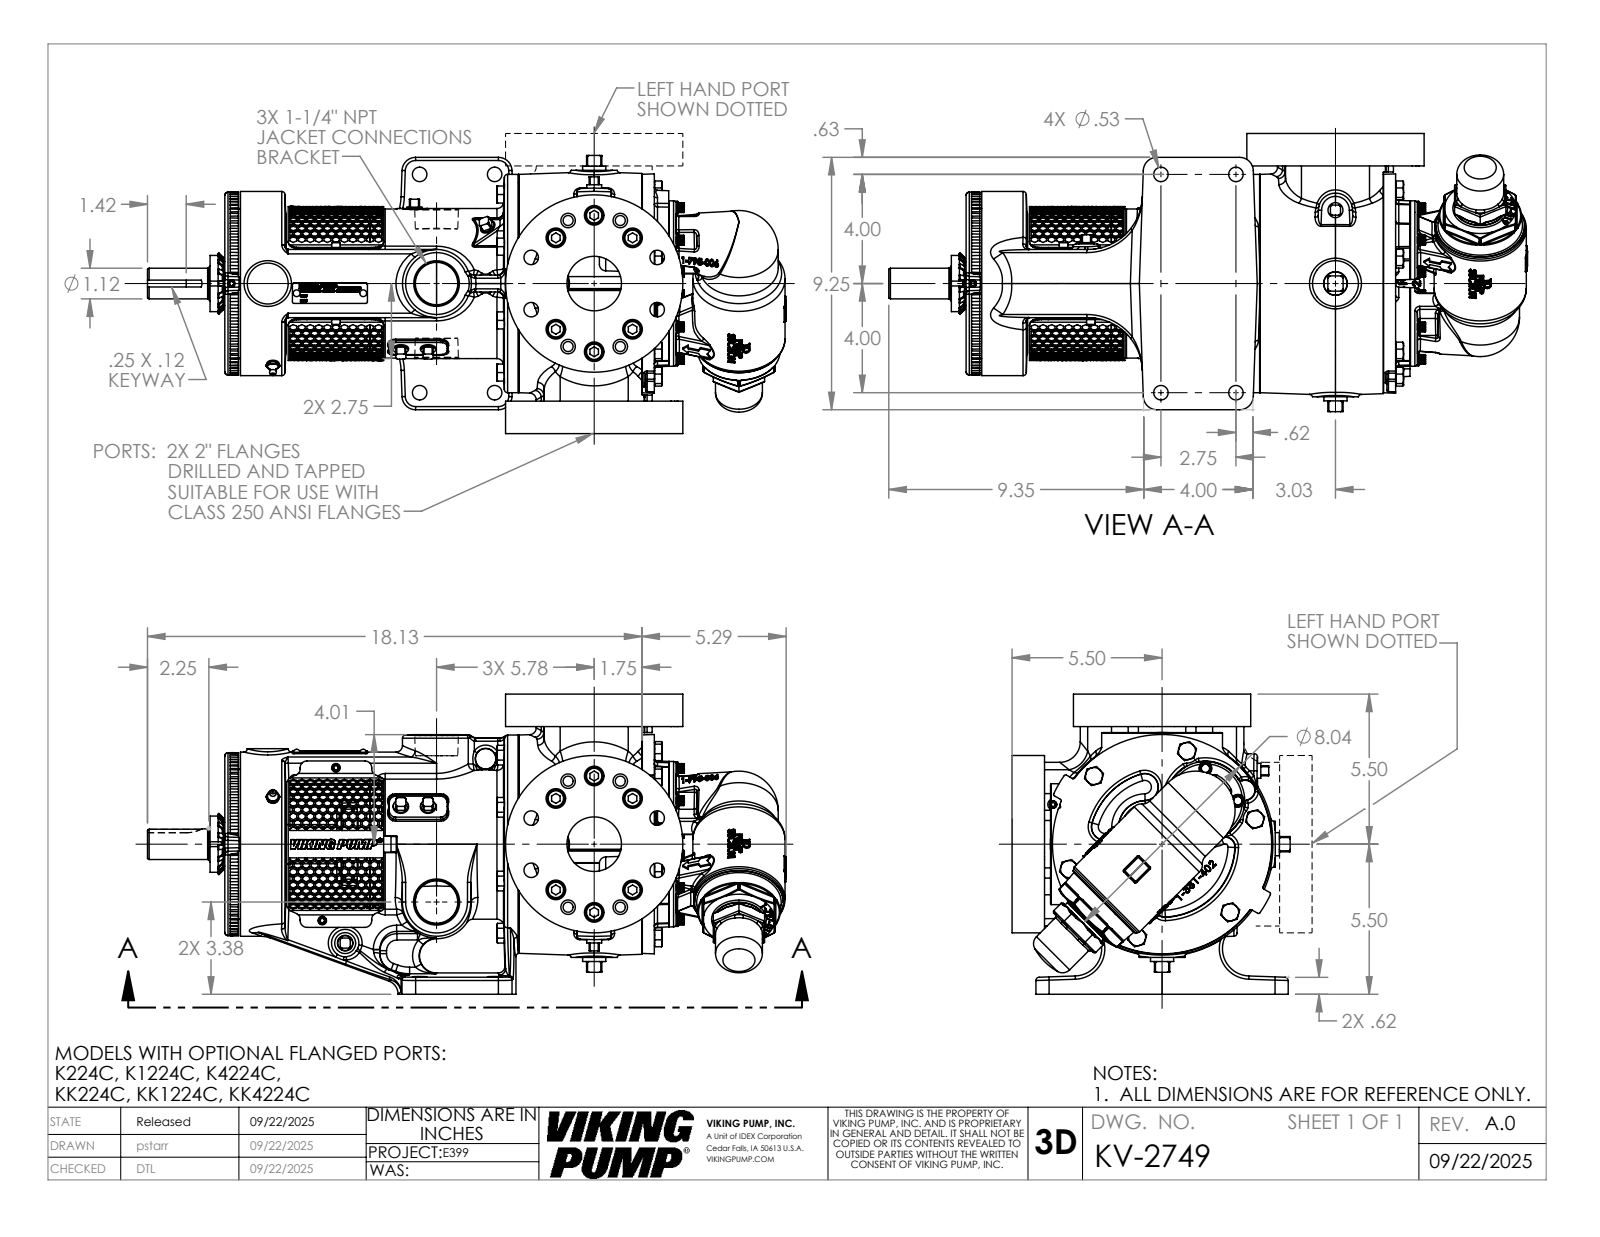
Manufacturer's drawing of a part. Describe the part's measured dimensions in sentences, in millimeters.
The part is named "KV-2749". Its 3-D file was written by "SolidWorks 2024 (AUTOMOTIVE_DESIGN)". It is 1 solid with 5661 faces: 1997 planar, 775 cylindrical and 2889 other. Overall it measures 594.8 by 279.4 by 259 millimeters. Its volume is 11 630 000 cubic millimeters and its surface area 776 100 square millimeters. Round holes: 16 of diameter 13.5, 12 of diameter 18.3, 9 of diameter 6.4, 8 of diameter 9.3, 8 of diameter 19.8, 6 of diameter 5, 4 of diameter 13.5, 2 of diameter 4, 2 of diameter 8, 2 of diameter 50.8, 1 of diameter 6.5, 1 of diameter 11.5. Round bosses or shafts: 23 of diameter 15.9, 8 of diameter 11.9, 3 of diameter 73.2, 3 of diameter 15.9, 3 of diameter 7.9, 3 of diameter 4.8, 2 of diameter 165.1, 1 of diameter 203.2. Partial cylindrical surfaces (rounded edges, fillets, slot ends): 39 of radius 3, 37 of radius 0.8, 22 of radius 6.1, 18 of radius 25.4, 16 of radius 3, 8 of radius 2.3, 8 of radius 4.5, 8 of radius 6.4. The main face-to-face distances are 279.4, 30.2, 264.8, 135.2, 400, 14.6, 120.7, 385.4, 249.2, 12.7. The hole center spacings are 63.5, 76.2, 26.2, 48.6, 24.8, 29.3, 35, 55.5.
